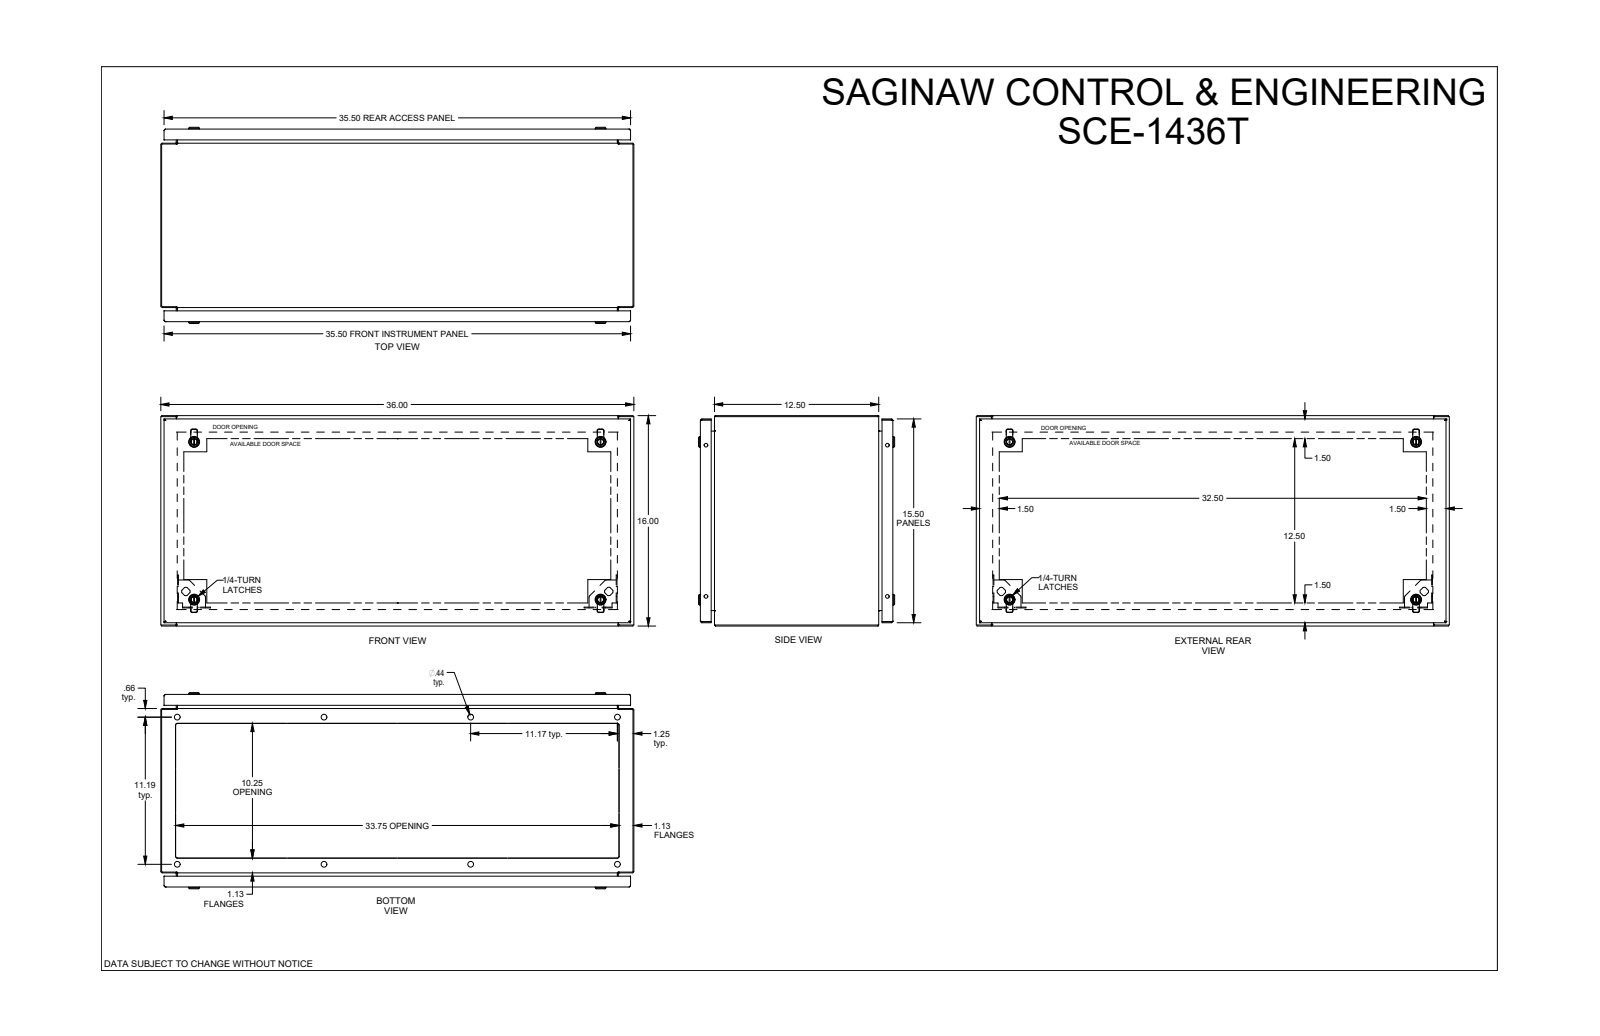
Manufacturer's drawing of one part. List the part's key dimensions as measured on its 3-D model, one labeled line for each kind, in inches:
Part name (STEP PRODUCT): SCE-1436T
STEP written by: SolidWorks 2019 (AUTOMOTIVE_DESIGN)
Units: inches
Bodies: 52 solids, 3130 faces (1498 planar, 1248 cylindrical, 384 other)
Overall size (bounding box): 36 × 16 × 14.924
Volume: 199.3 in³ · Surface area: 5 575 in²
Round holes (diameter × count): ⌀0.437 ×8, ⌀0.165 ×4, ⌀0.236 ×4, ⌀0.319 ×4, ⌀0.472 ×4, ⌀0.634 ×4
Round bosses / shafts (diameter × count): ⌀0.827 ×4, ⌀0.787 ×4, ⌀0.551 ×4, ⌀0.465 ×4, ⌀0.425 ×4, ⌀0.362 ×4, ⌀0.315 ×4, ⌀0.189 ×4
Partial cylindrical surfaces — rounded edges, fillets, slot ends (radius × count): R0.012 ×120, R0.02 ×70, R0.02 ×56, R0.125 ×26, R0.015 ×20, R0.042 ×16, R0.103 ×16, R0.117 ×16
Main face-to-face distances: 0.06, 14.588, 0.075, 14.648, 14.528, 0.075, 35.925, 13.499, 1.074, 1.175
Hole centre spacings: 11.167, 11.187, 15.807, 22.333, 24.979, 11.167, 12, 15.807
